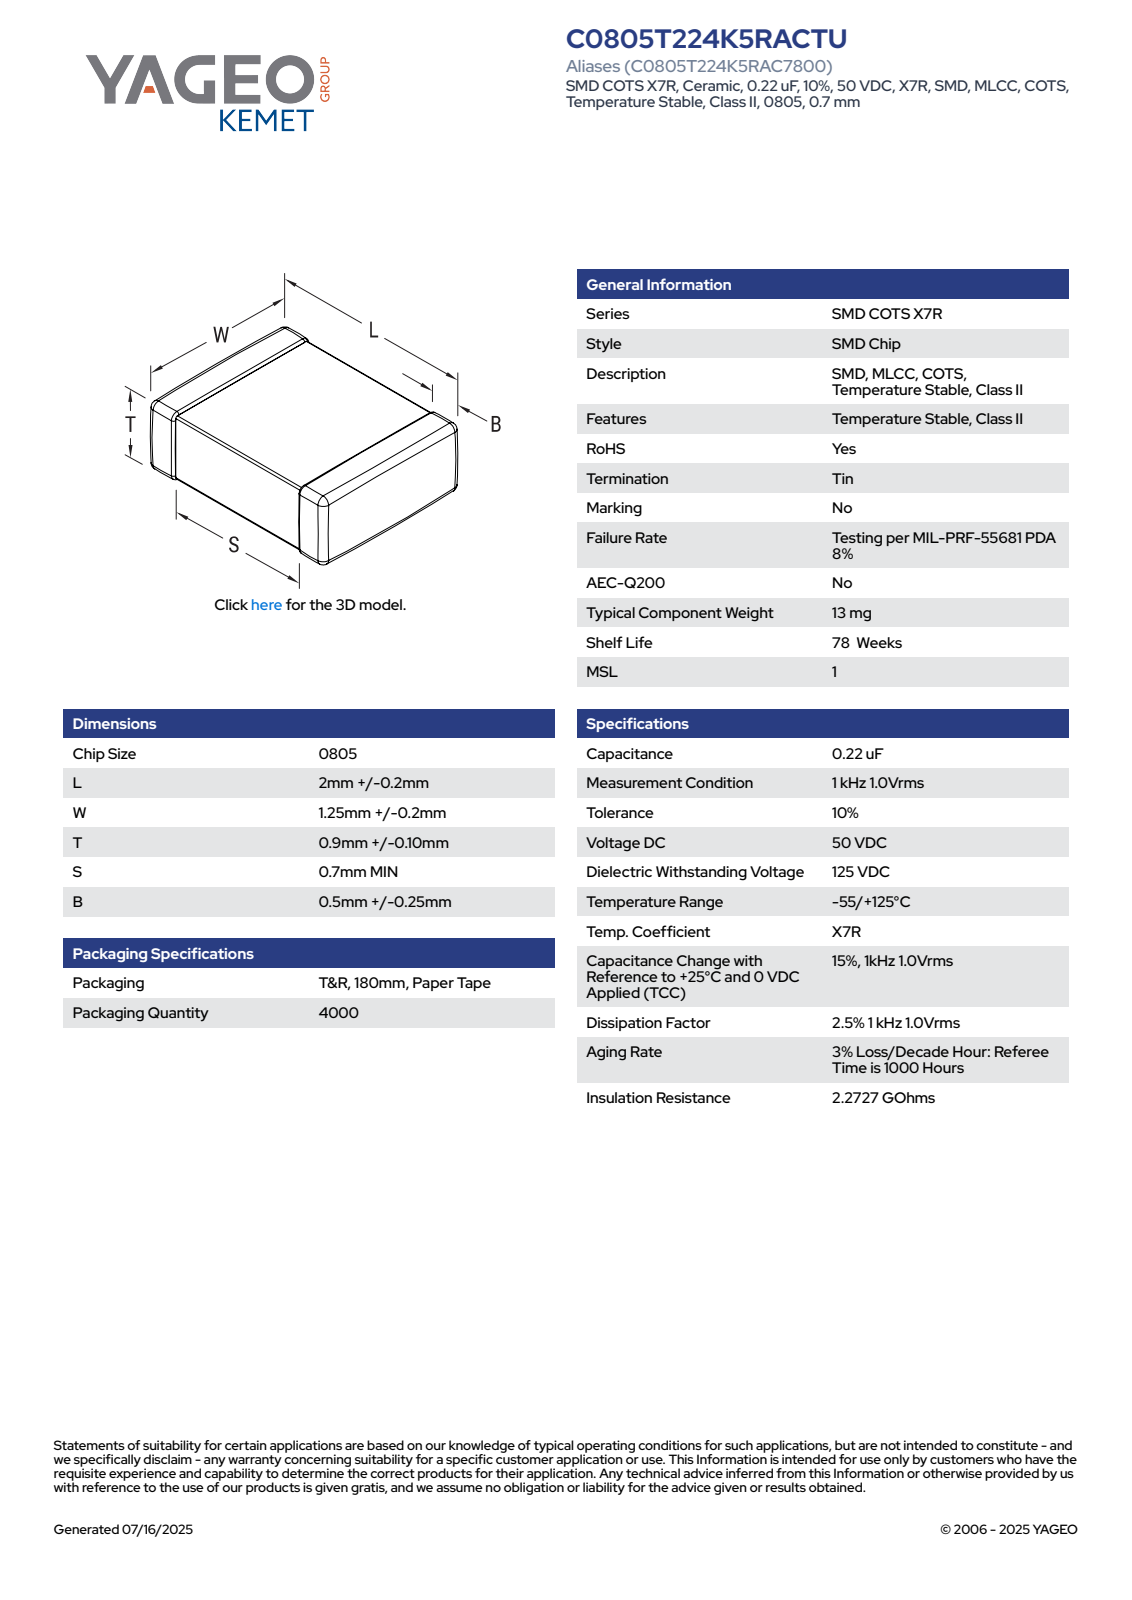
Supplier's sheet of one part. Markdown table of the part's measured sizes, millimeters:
| quantity | value |
| --- | --- |
| part name | CCSM_STD_0805_L2.2W1.45T1S0.9B0.75 |
| STEP written by | SolidWorks 2021 (AUTOMOTIVE_DESIGN) |
| units | millimeters |
| bodies | 4 solids, 121 faces (71 planar, 34 cylindrical, 16 other) |
| overall size | 2.2 × 1.45 × 1 |
| volume | 3 mm³ |
| surface area | 14 mm² |
| main face-to-face distances | 0.97, 1, 2.2, 1.45, 1.42, 0.94, 1.39, 1.23, 1.19, 1.01 |
